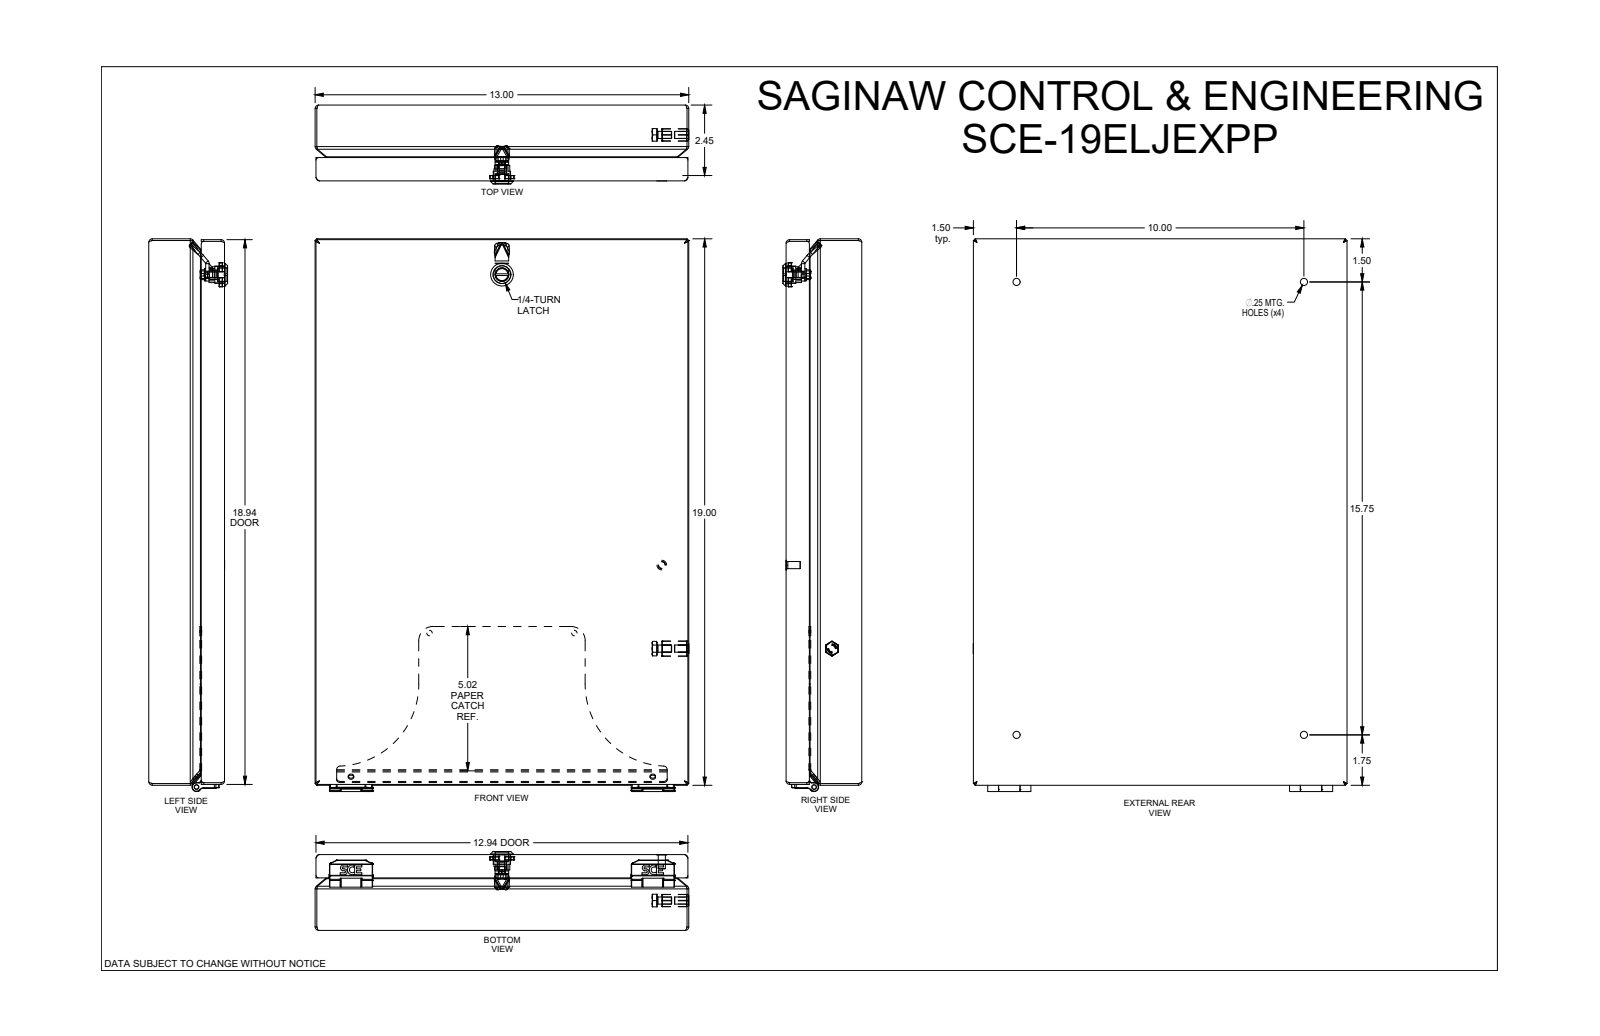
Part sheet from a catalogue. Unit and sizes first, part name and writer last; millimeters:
Units: millimetres
Overall size (bounding box): 488.2 × 330.3 × 72.2
Round holes (diameter × count): ⌀4.7 ×4, ⌀7.2 ×4, ⌀0.5 ×2, ⌀2.5 ×2, ⌀4.8 ×2, ⌀8.4 ×2, ⌀4 ×1, ⌀5.1 ×1, ⌀6.1 ×1, ⌀6.1 ×1, ⌀6.5 ×1, ⌀6.8 ×1
Round bosses / shafts (diameter × count): ⌀8.6 ×2, ⌀6.6 ×2, ⌀6.3 ×2, ⌀4.6 ×2, ⌀20 ×1, ⌀13.9 ×1, ⌀11.7 ×1, ⌀11.1 ×1
Partial cylindrical surfaces — rounded edges, fillets, slot ends (radius × count): R0.2 ×32, R0.8 ×28, R0.4 ×26, R0.3 ×21, R1.3 ×16, R1.5 ×11, R0.3 ×10, R1.6 ×8
Main face-to-face distances: 1.5, 1.5, 66.9, 65.4, 65.4, 63.9, 1.5, 20.3, 328.7, 0.8
Hole centre spacings: 137.1, 143.2, 235.3, 285.8, 322.9, 335.4, 386.2, 438.2
Volume: 800 800 mm³ · Surface area: 1 014 000 mm²
Bodies: 20 solids, 878 faces (310 planar, 376 cylindrical, 192 other)
Part name (STEP PRODUCT): SCE-19ELJEXPP_REV1
STEP written by: SolidWorks 2021 (AUTOMOTIVE_DESIGN)
